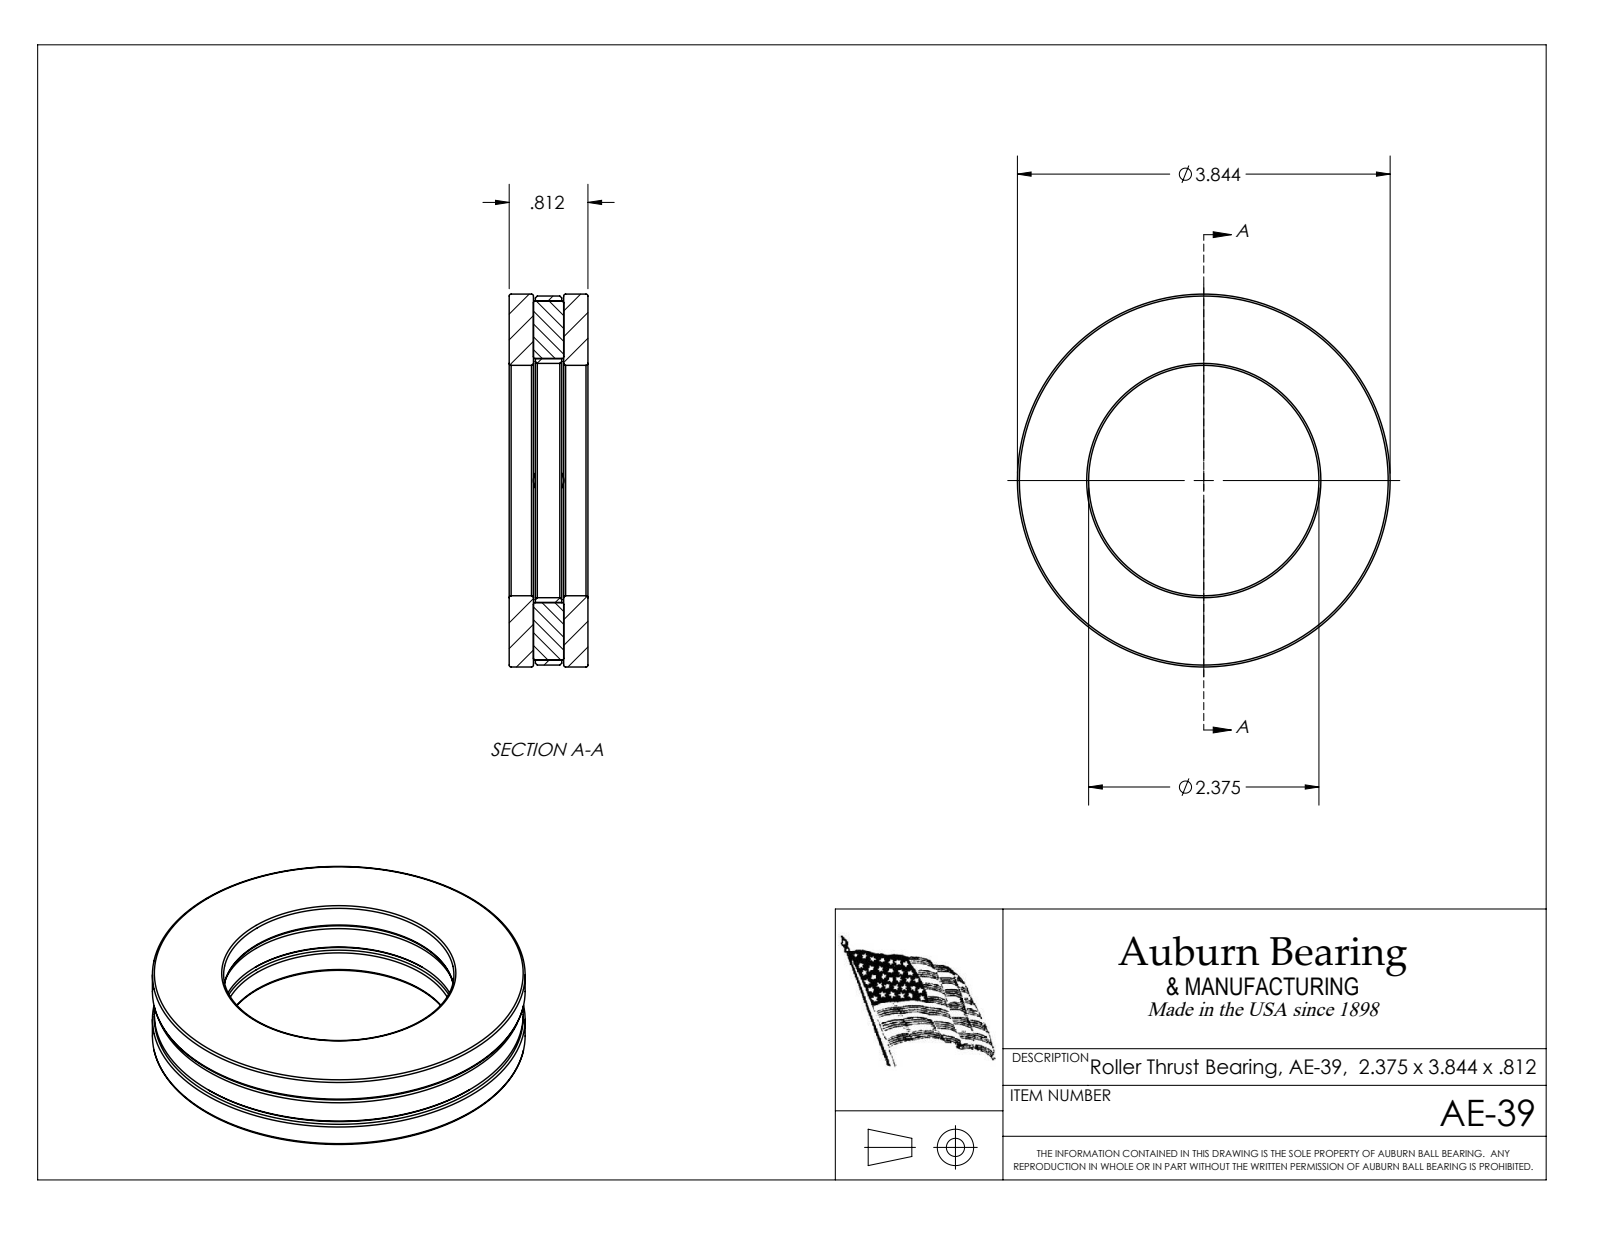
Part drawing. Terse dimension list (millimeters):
name: AE-39
written by: SolidWorks 2017 (CONFIG_CONTROL_DESIGN)
unit: mm
bodies: 7 solids, 60 faces (30 planar, 10 cylindrical, 20 other)
size: 97.6 × 97.6 × 20.6
volume: 88 440 mm³; area: 38 440 mm²
holes: 1× ⌀60.3, 1× ⌀61.3
bosses: 2× ⌀7.9, 1× ⌀97.6, 1× ⌀96.6
face distances: 6.4, 14.3, 6.9, 13.8, 0.5, 7.4, 7.9, 20.6, 6.9, 28
